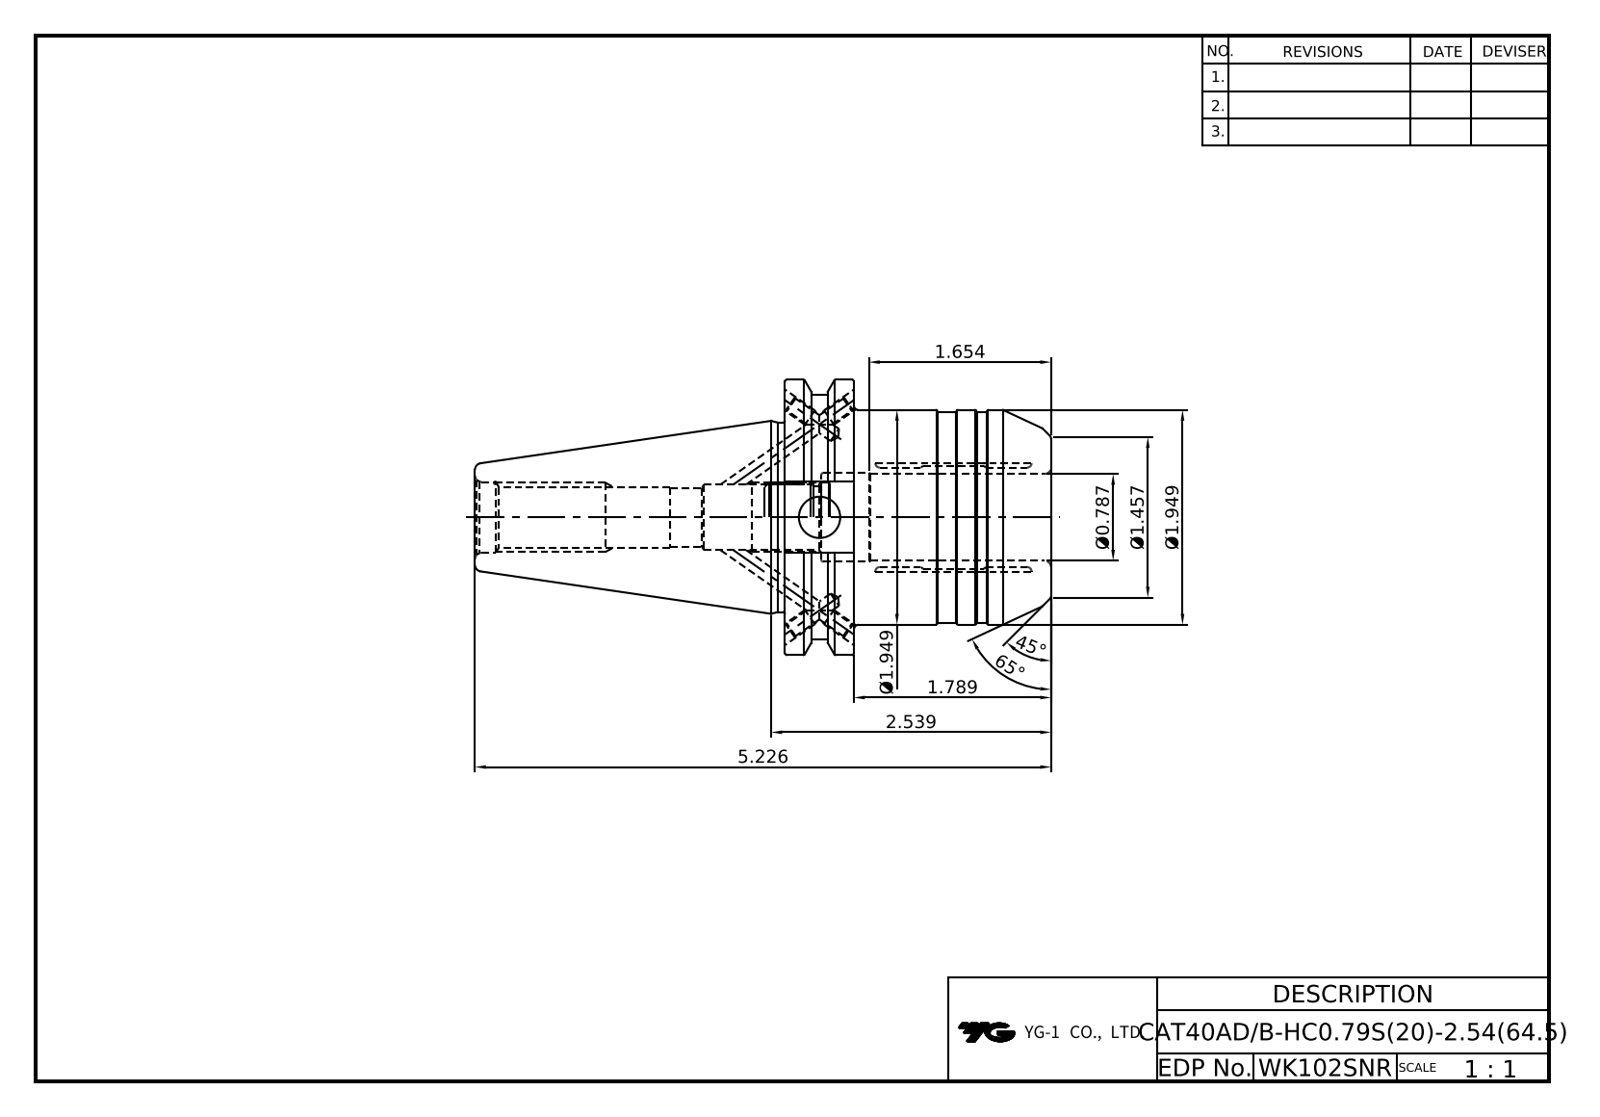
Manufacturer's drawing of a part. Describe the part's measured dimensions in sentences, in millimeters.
The part is named "LO-CAT40ADB-HC20S-64.5". Its 3-D file was written by "Autodesk Inventor 2025 (AUTOMOTIVE_DESIGN)". It is 1 solid with 106 faces: 34 planar, 31 cylindrical and 41 other. Overall it measures 132.75 by 63.5 by 61.09 millimeters. Its volume is 166 753 cubic millimeters and its surface area 30 429 square millimeters. Round holes: 4 of diameter 3.24, 4 of diameter 4, 1 of diameter 9.53, 1 of diameter 13.39, 1 of diameter 13.84, 1 of diameter 16.3, 1 of diameter 20, 1 of diameter 20.4. Round bosses or shafts: 1 of diameter 63.5, 1 of diameter 56.3, 1 of diameter 49.5, 1 of diameter 48.5, 1 of diameter 43.6. Partial cylindrical surfaces (rounded edges, fillets, slot ends): 1 of radius 8.19. The main face-to-face distances are 61.33, 15.88, 45.45, 8.33, 7.55, 53, 47.6, 16.38, 71.42, 79.75. The hole center spacings are 35.13.
